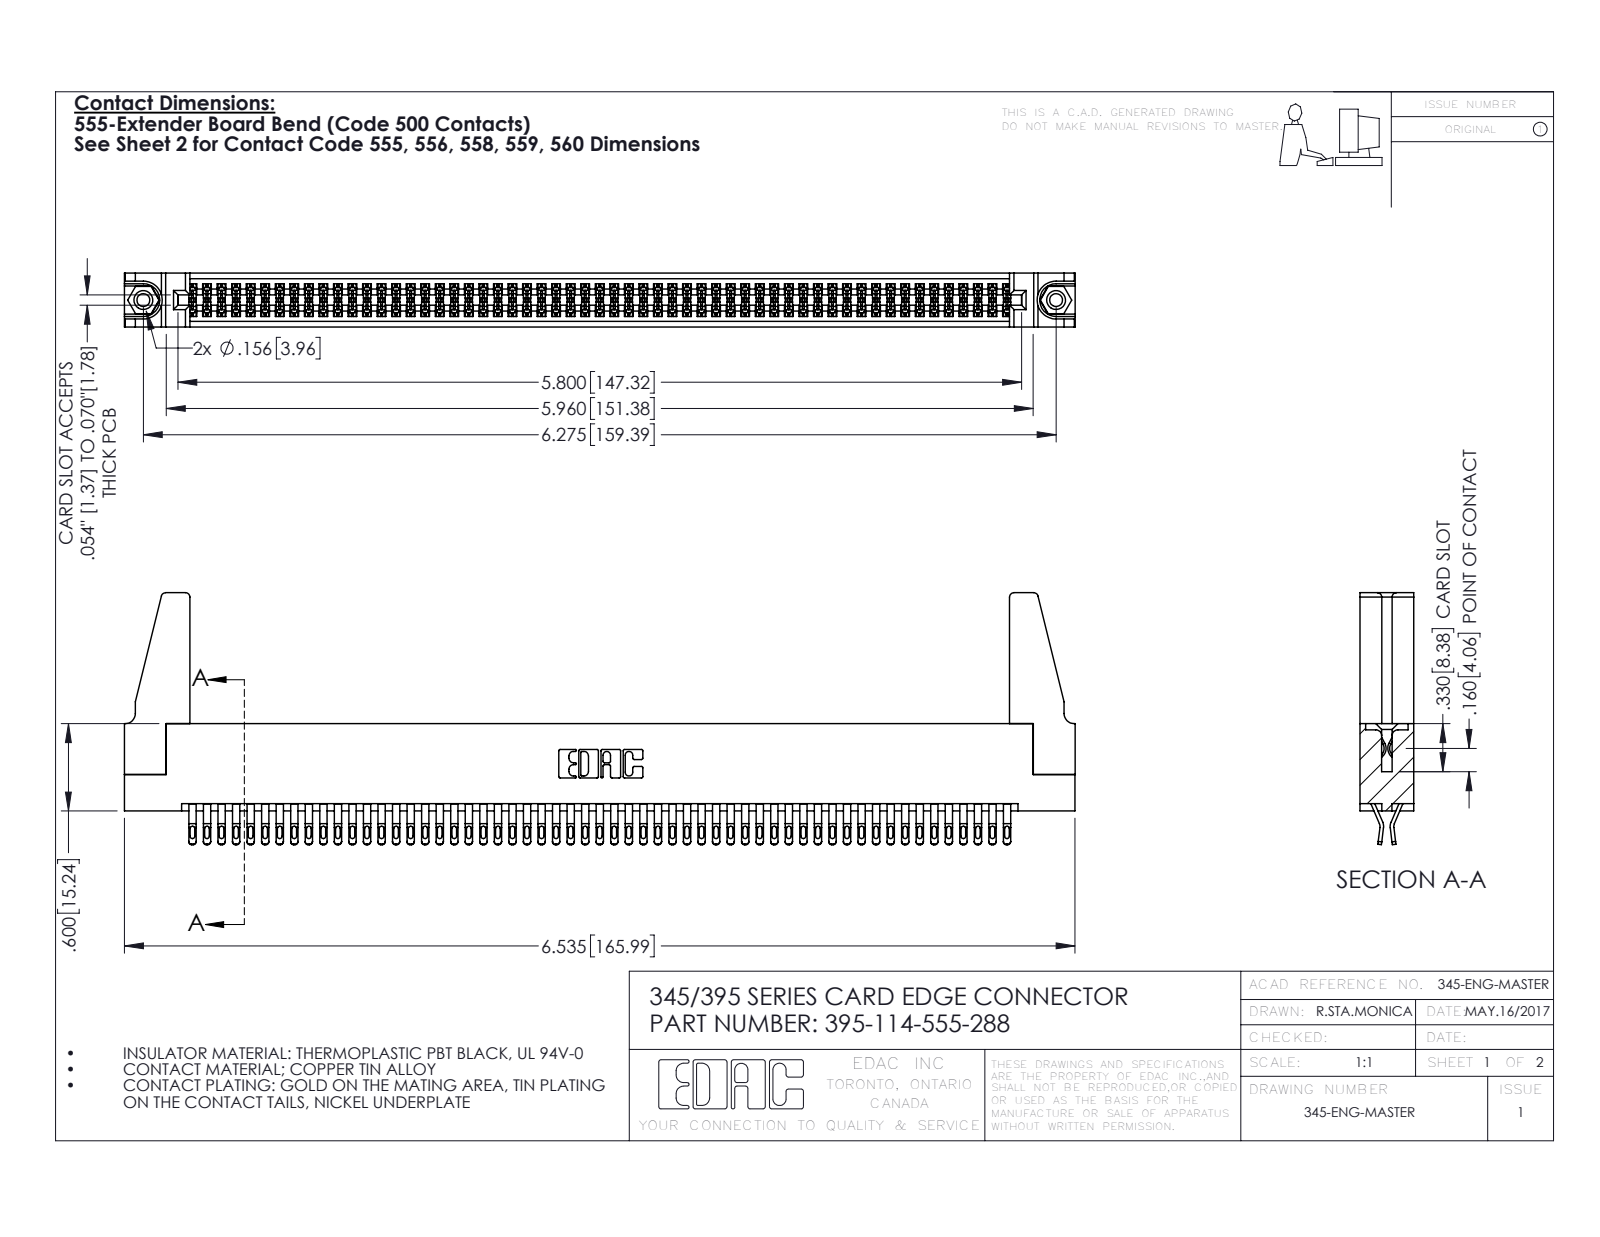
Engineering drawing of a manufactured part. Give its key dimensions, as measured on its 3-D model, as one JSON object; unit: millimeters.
{"part_name": "345-250-001_345-250-001-102; 395-114-555-288; 345-220-078_345-220-088; 345 Part_Flush Mounting Lugs - 0.156 Dia-TH (+1 more)", "step_written_by": "SolidWorks 2016 (CONFIG_CONTROL_DESIGN)", "units": "millimeters", "bodies": {"solids": 119, "faces": 6634, "planar": 3686, "cylindrical": 2932, "other": 16}, "overall_size": [166, 44, 9.4], "volume_mm3": 19840, "surface_area_mm2": 29100, "round_holes": [[2.3, 2], [3.2, 2], [4, 2], [1.6, 1]], "round_bosses_or_shafts": [[3.9, 2]], "partial_cylinders_radius": [[0.4, 285], [0.5, 228], [0.2, 171], [0.3, 22], [0.8, 8], [0.2, 6], [0.8, 6], [0.7, 3]], "face_to_face_distances": [1.8, 7.6, 9.4, 0.6, 5.1, 2.5, 6.9, 5.7, 4.4, 3.8], "hole_center_spacings": [6.9, 153.4, 159.4]}
